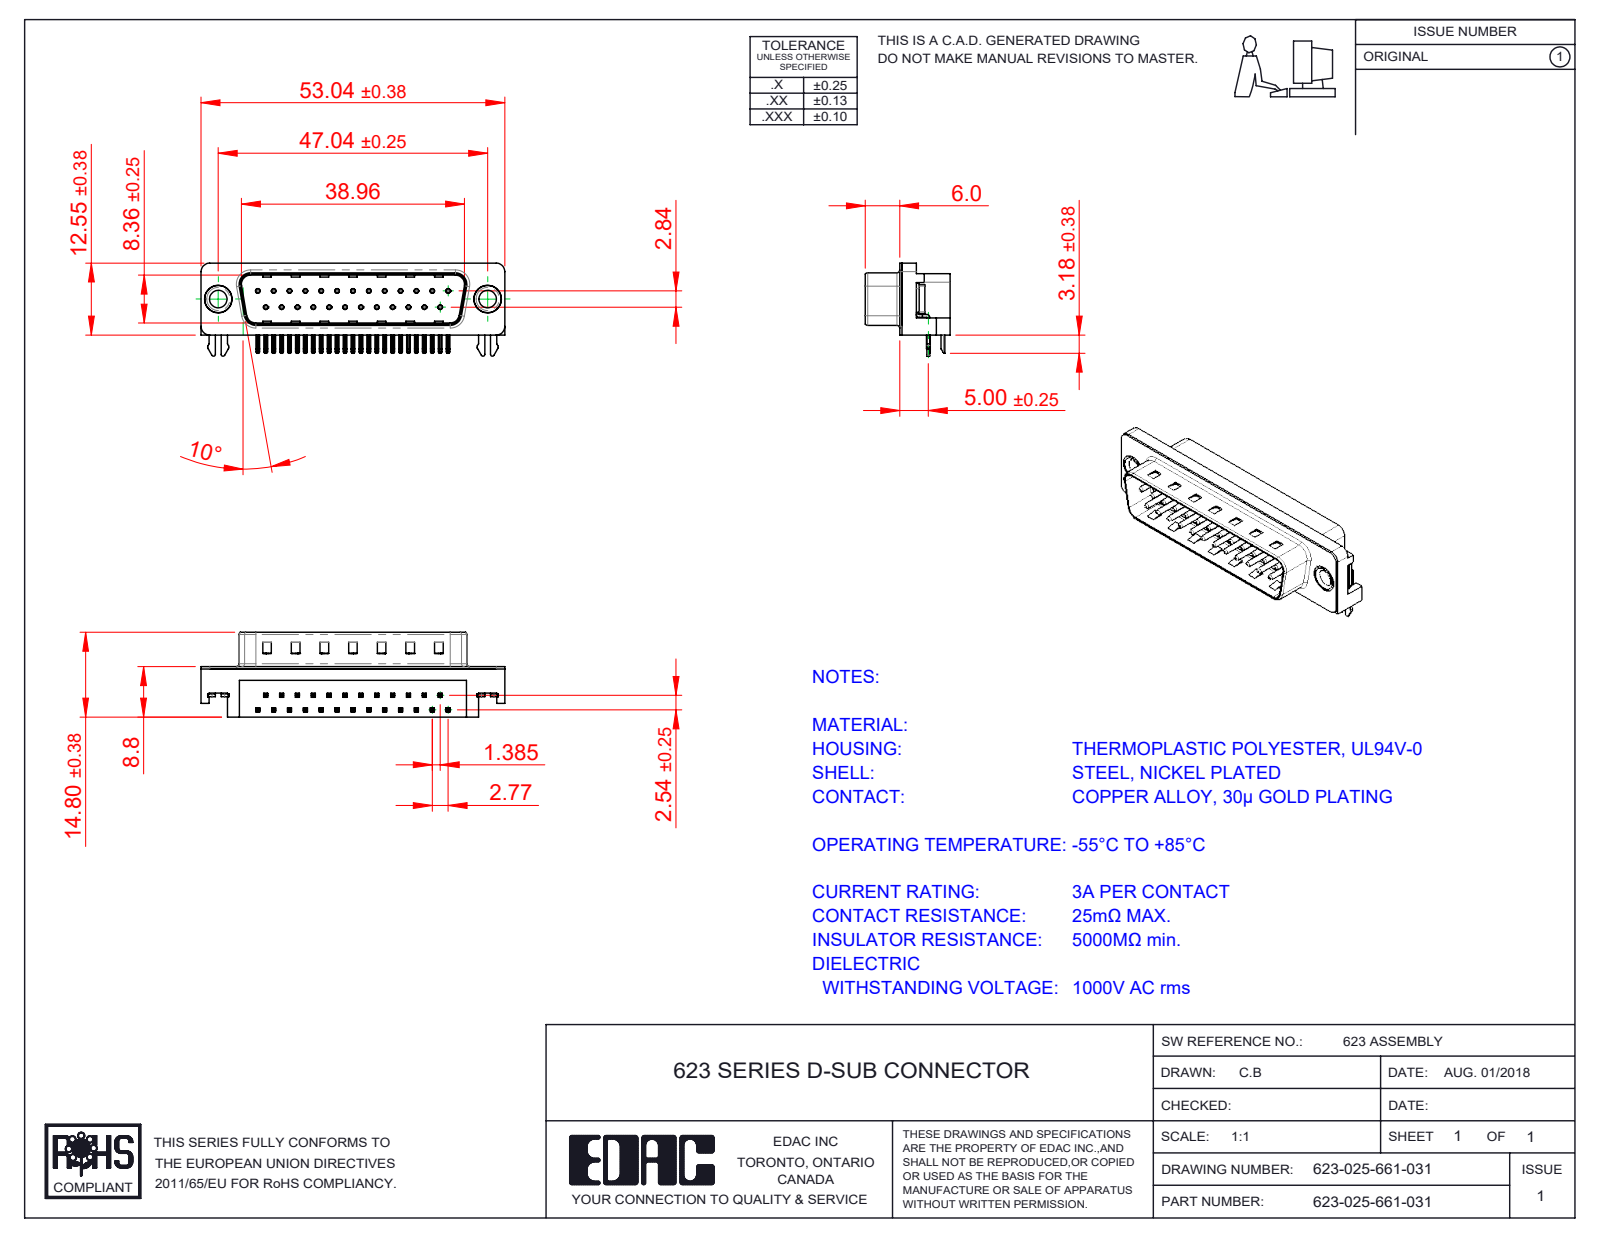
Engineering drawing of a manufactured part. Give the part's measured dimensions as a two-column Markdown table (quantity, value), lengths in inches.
| quantity | value |
| --- | --- |
| part name | 623 Housing_25 Socket; 623 Contact Bottom; 623 Shell_25 Socket; 623-025-661-031 (+3 more) |
| STEP written by | SolidWorks 2016 (CONFIG_CONTROL_DESIGN) |
| units | inches |
| bodies | 31 solids, 2245 faces (1433 planar, 635 cylindrical, 177 other) |
| overall size | 2.088 × 0.64 × 0.583 |
| volume | 0.288 in³ |
| surface area | 10.47 in² |
| round holes (diameter × count) | 0.014 × 25, 0.031 × 25, 0.12 × 2, 0.157 × 2, 0.189 × 2, 0.197 × 2 |
| round bosses / shafts (diameter × count) | 0.03 × 25, 0.193 × 2, 0.187 × 2, 0.152 × 2 |
| partial cylindrical surfaces (radius × count) | 0.01 × 108, 0.005 × 50, 0.02 × 14, 0.039 × 8, 0.059 × 7, 0.013 × 4, 0.035 × 4, 0.063 × 4 |
| main face-to-face distances | 0.016, 0.331, 0.083, 0.067, 0.345, 0.412, 0.428, 0.407, 0.346, 0.232 |
| hole center spacings | 0.124, 0.109, 0.436, 0.218, 0.327, 0.198, 0.545, 0.294 |
